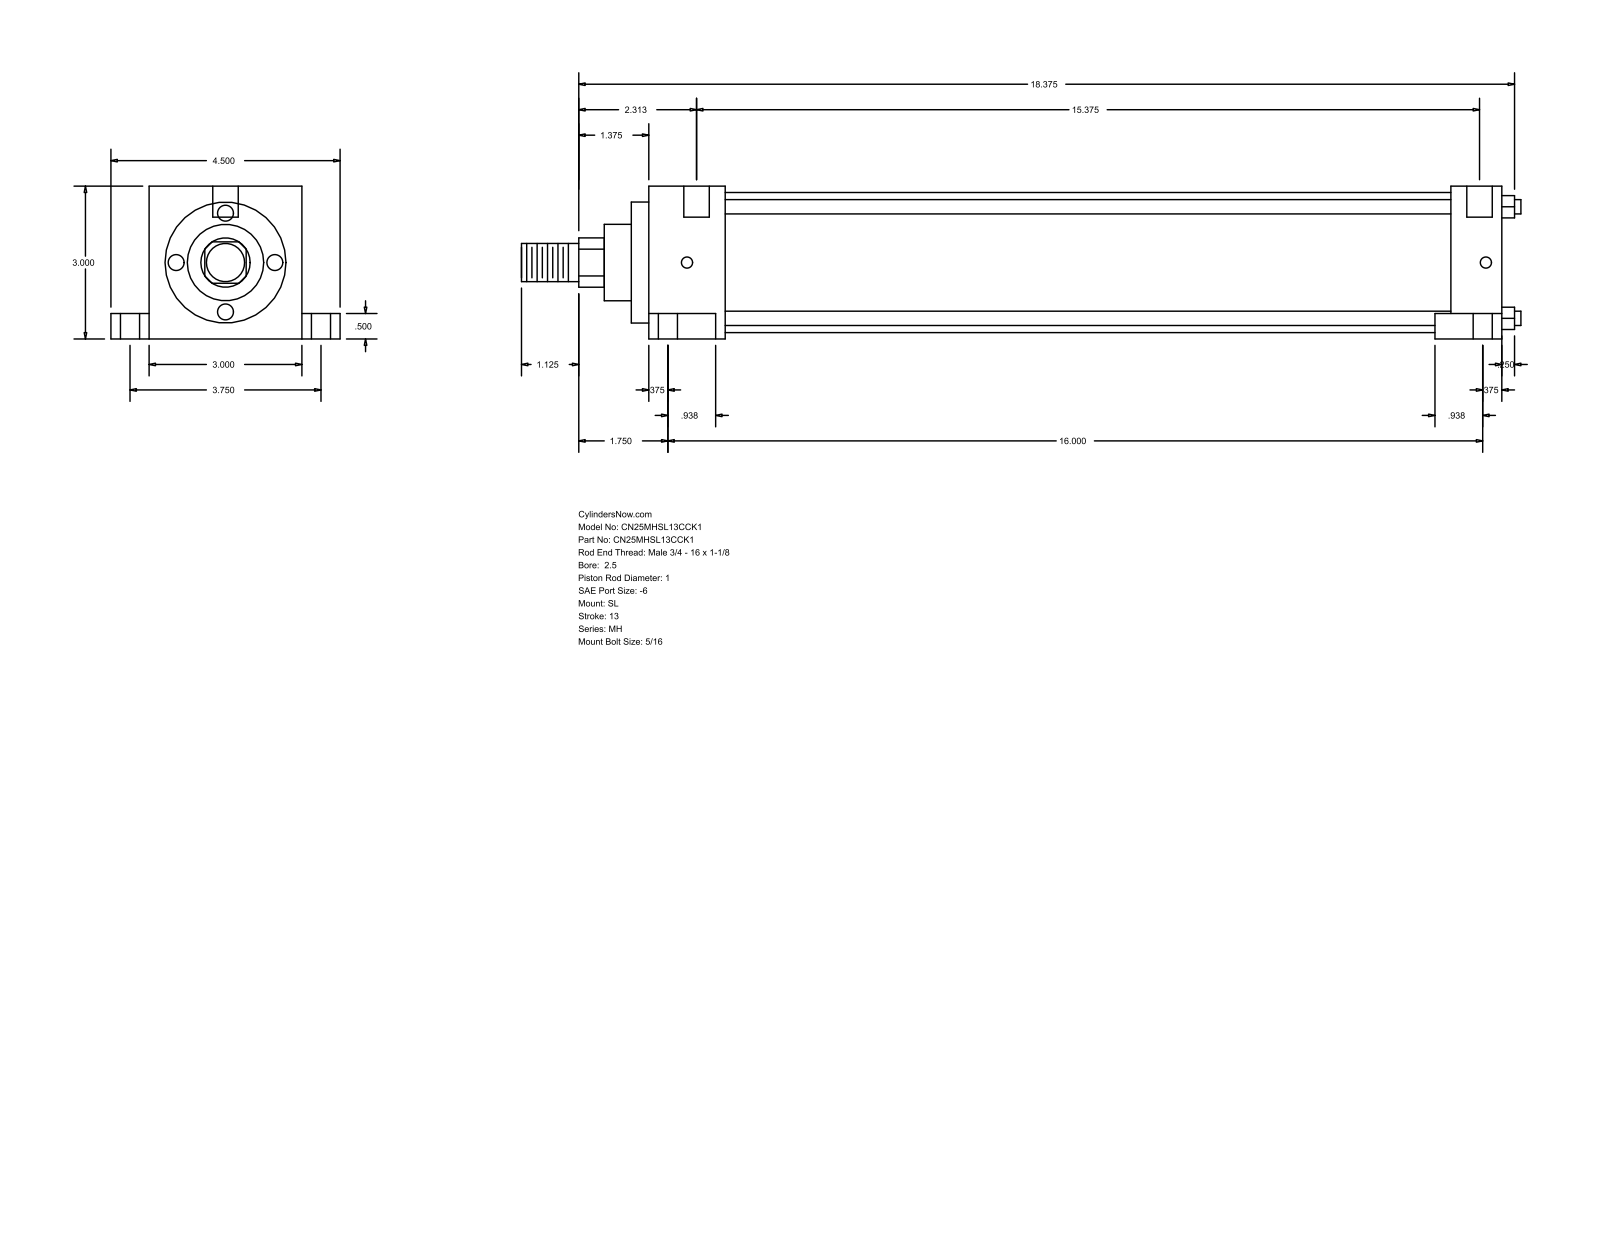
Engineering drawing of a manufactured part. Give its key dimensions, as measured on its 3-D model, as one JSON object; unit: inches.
{"part_name": "MH_SL__0250_1", "step_written_by": "GSSL Pune (CONFIG_CONTROL_DESIGN)", "units": "inches", "bodies": {"solids": 0, "faces": 86, "planar": 61, "cylindrical": 25, "other": 0}, "overall_size": [19.625, 4.5, 3], "round_holes": [[0.219, 2], [0.375, 2], [0.625, 2], [0.5, 1]], "round_bosses_or_shafts": [[0.281, 4], [2.75, 1], [2.375, 1], [1.5, 1], [1, 1], [0.75, 1]], "partial_cylinders_radius": [[0.484, 1]], "face_to_face_distances": [3, 1, 16.094, 17.094, 0.5, 2.5, 0.75, 3.75, 0.531, 16.625], "hole_center_spacings": [1.876, 0.125, 3.75]}
